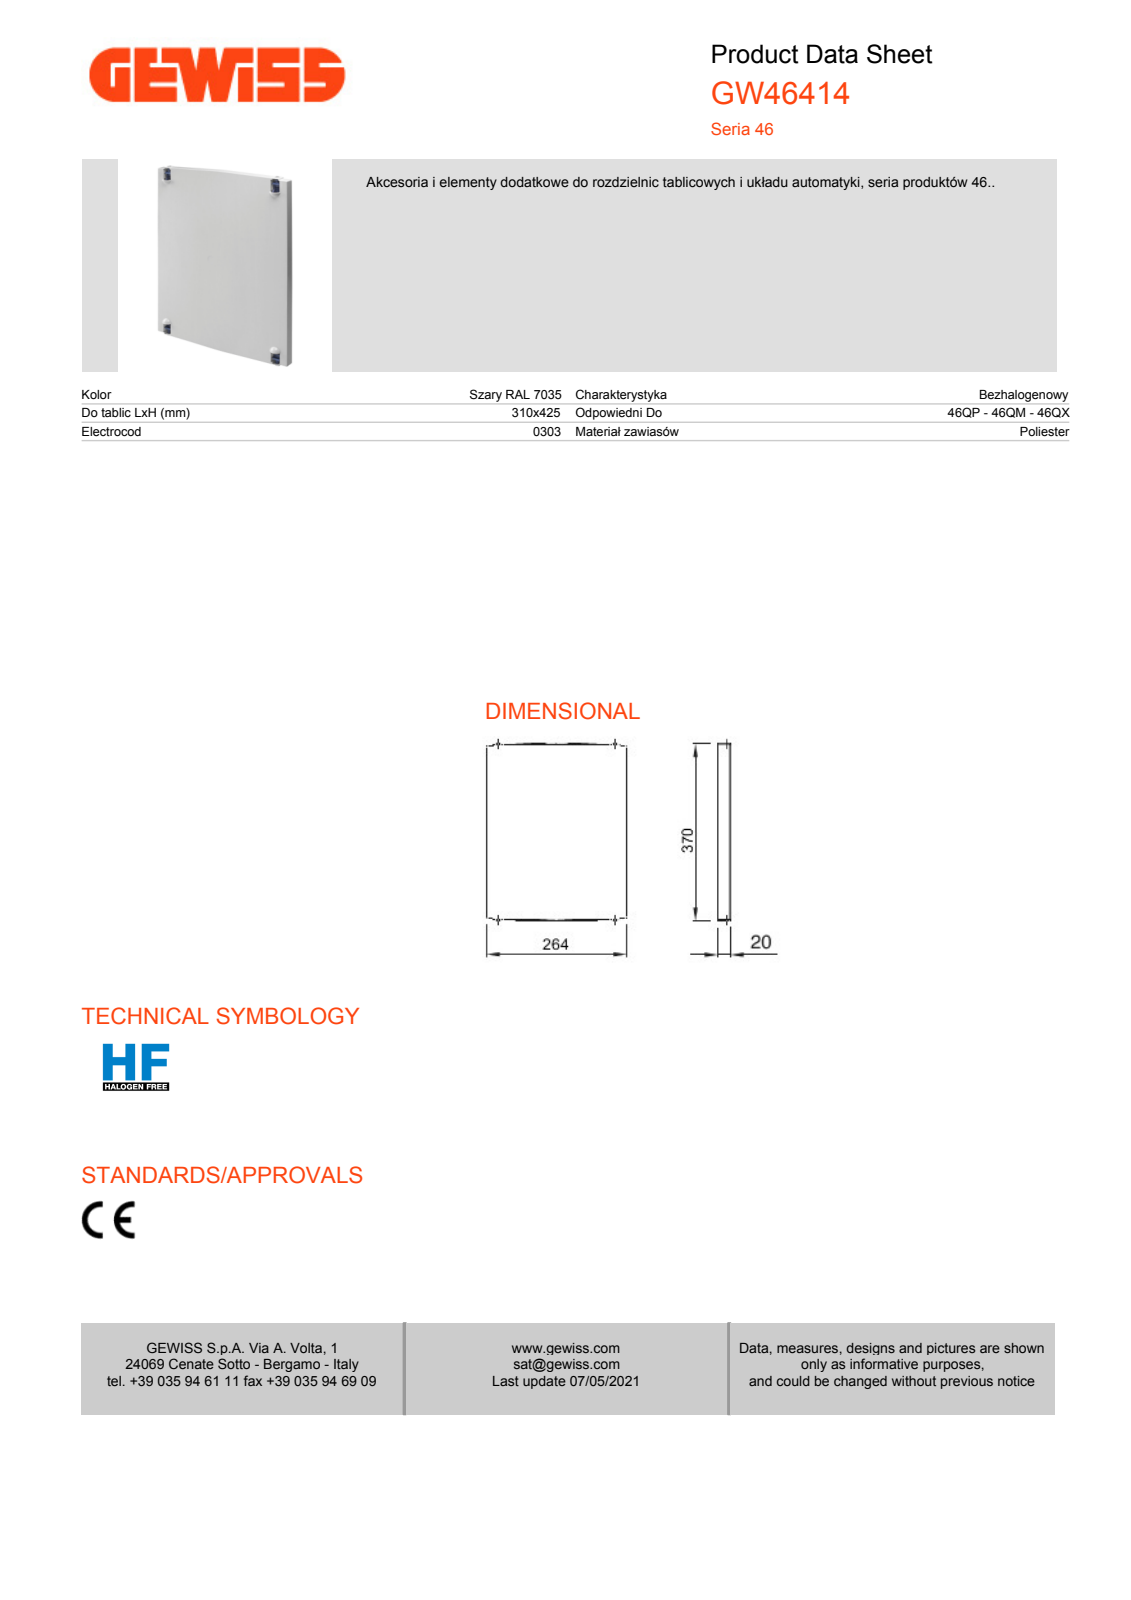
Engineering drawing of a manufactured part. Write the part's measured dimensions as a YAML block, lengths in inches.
part_name: "GW46414"
step_written_by: "CREO PARAMETRIC BY PTC INC, 2020354 (CONFIG_CONTROL_DESIGN)"
units: inches
bodies: {solids: 1, faces: 207, planar: 131, cylindrical: 52, other: 24}
overall_size: [14.837, 10.388, 1.194]
volume: 18.36
surface_area: 390.7
round_holes:
  - {diameter: 0.331, count: 2}
round_bosses_or_shafts:
  - {diameter: 0.476, count: 2}
partial_cylinders:
  - {radius: 0.079, count: 20}
  - {radius: 0.02, count: 4}
  - {radius: 0.118, count: 4}
  - {radius: 0.197, count: 2}
face_to_face_distances: [0.098, 0.689, 0.787, 0.591, 7.953, 1.561, 9.513, 0.685, 7.945, 8.63]
hole_center_spacings: [7.953]
